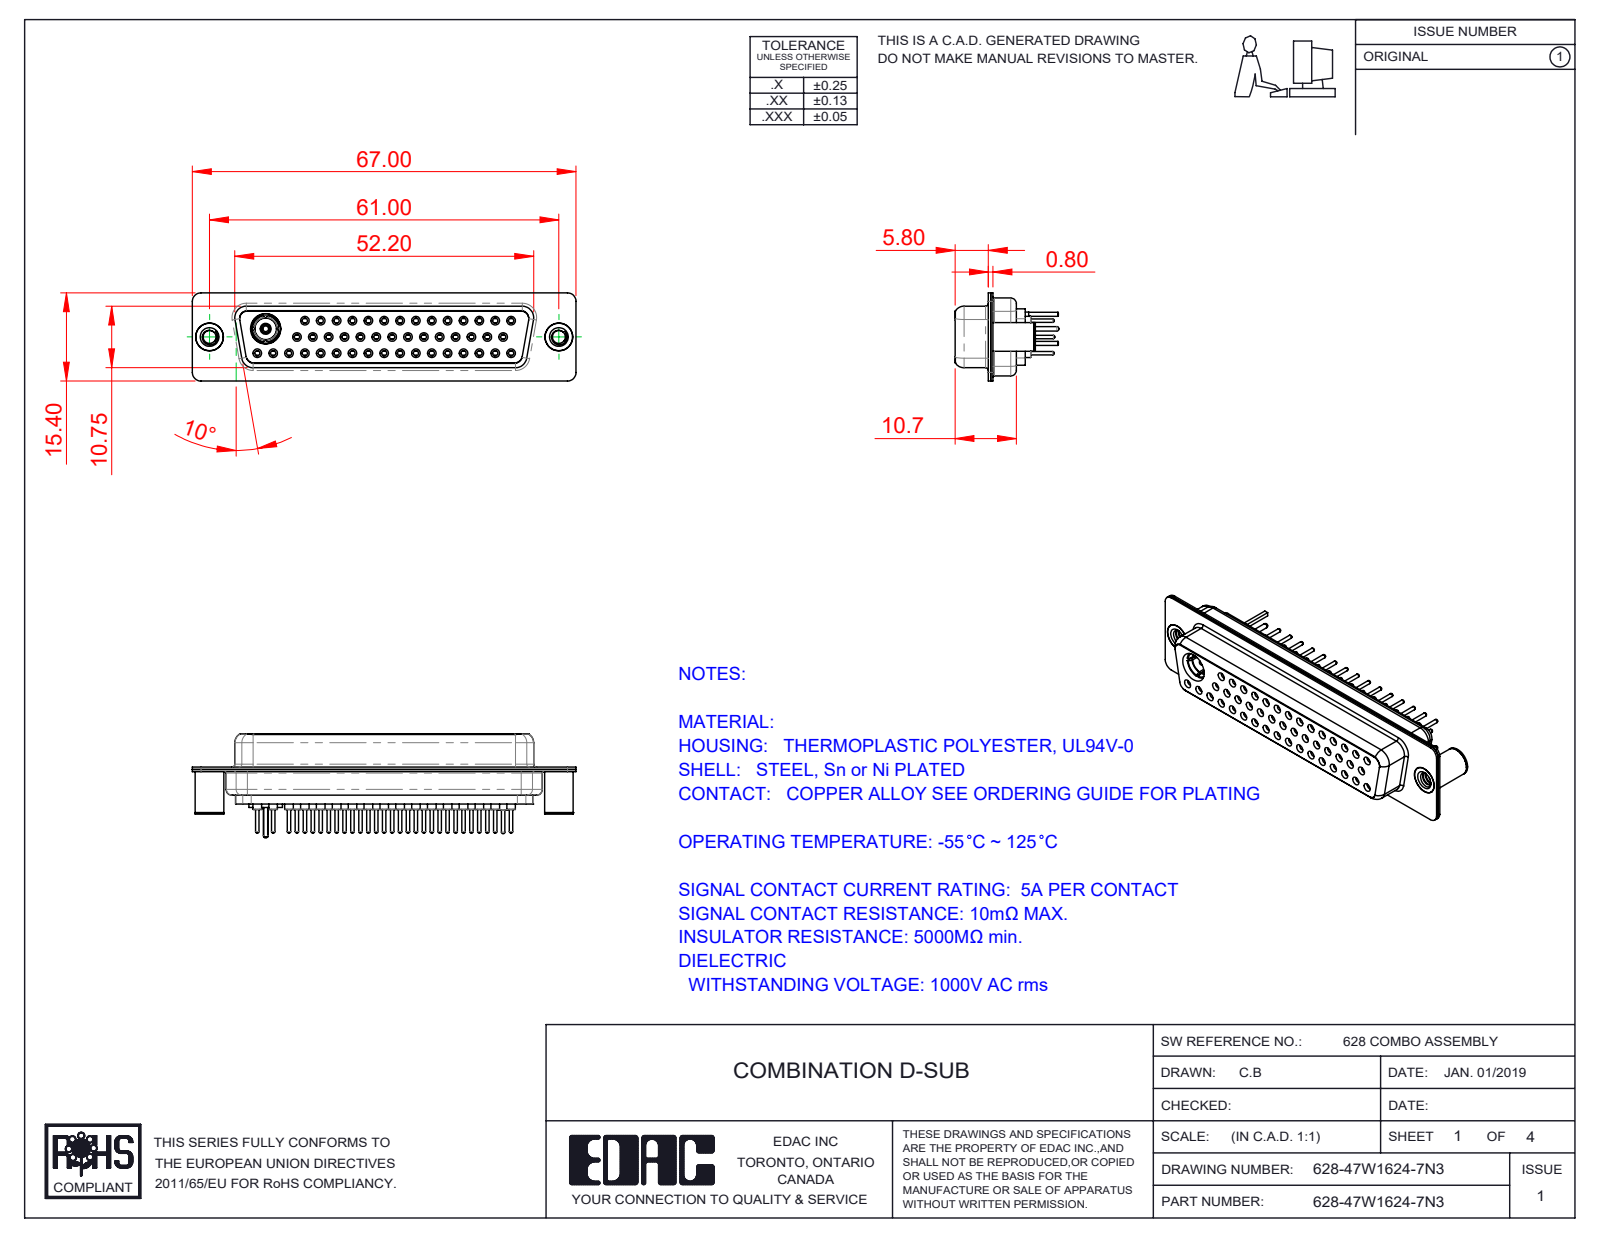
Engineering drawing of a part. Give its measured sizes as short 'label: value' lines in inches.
name: Locking Collar; 628Combo Shell Rear_50 Contacts; Insulator Pin_Straight PC Tail; Co-Ax Plug Assy_St (+8 more)
written by: SolidWorks 2016 (CONFIG_CONTROL_DESIGN)
unit: in
bodies: 55 solids, 2957 faces (811 planar, 1072 cylindrical, 1074 other)
size: 2.638 × 0.715 × 0.606
volume: 0.437 in³; area: 23.46 in²
holes: 47× ⌀0.043, 46× ⌀0.059, 45× ⌀0.035, 45× ⌀0.079, 31× ⌀0.063, 14× ⌀0.067, 3× ⌀0.191, 2× ⌀0.089, 2× ⌀0.128, 2× ⌀0.157, 2× ⌀0.159, 1× ⌀0.111
bosses: 46× ⌀0.087, 46× ⌀0.024, 15× ⌀0.063, 3× ⌀0.197, 2× ⌀0.195, 2× ⌀0.189, 1× ⌀0.23, 1× ⌀0.205
rounds: 16× R0.059, 12× R0.053, 12× R0.079, 8× R0.063, 4× R0.01, 4× R0.02, 4× R0.024, 4× R0.026
face distances: 0.016, 0.238, 0.254, 0.446, 0.074, 0.482, 0.244, 0.228, 0.407, 0.43
hole spacings: 0.124, 0.109, 0.218, 0.327, 0.436, 0.545, 0.654, 0.763
